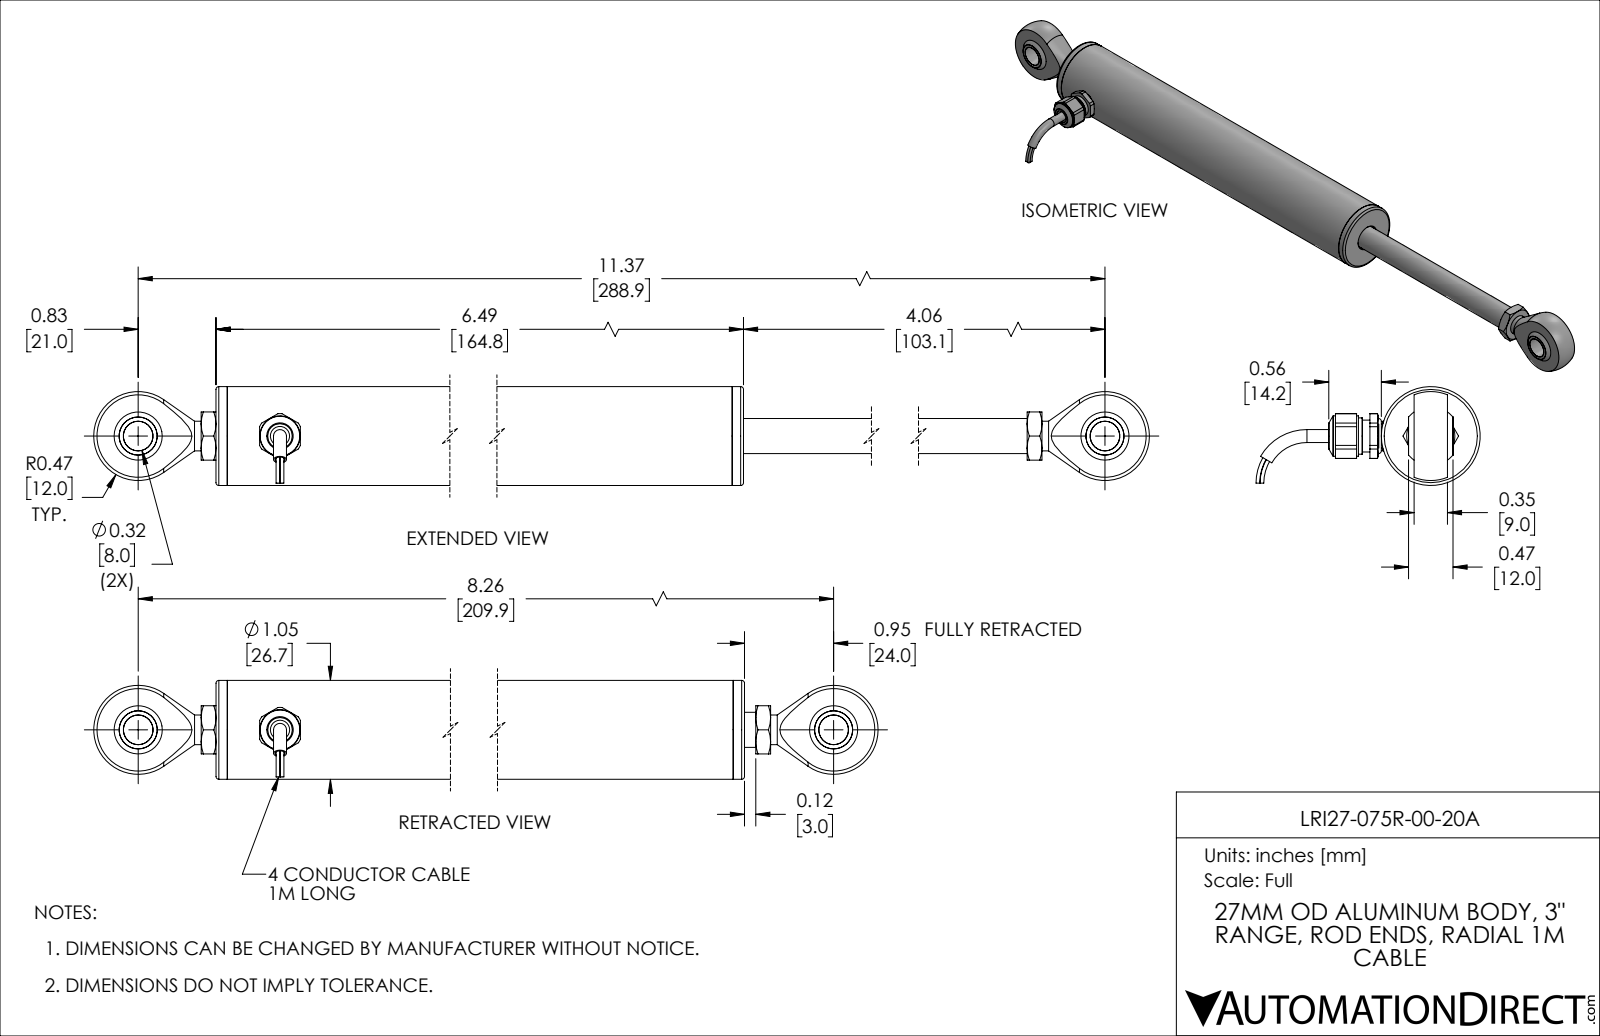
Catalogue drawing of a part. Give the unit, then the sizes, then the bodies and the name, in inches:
Units: inches
Overall size (bounding box): 9.208 × 2.382 × 1.05
Round holes (diameter × count): ⌀0.268 ×2, ⌀0.106 ×1, ⌀0.138 ×1, ⌀0.201 ×1, ⌀0.205 ×1, ⌀0.25 ×1, ⌀0.274 ×1, ⌀0.36 ×1, ⌀0.375 ×1, ⌀0.386 ×1, ⌀0.499 ×1, ⌀0.825 ×1
Round bosses / shafts (diameter × count): ⌀0.315 ×4, ⌀0.039 ×4, ⌀1.05 ×1, ⌀0.848 ×1, ⌀0.5 ×1, ⌀0.429 ×1, ⌀0.386 ×1, ⌀0.373 ×1
Partial cylindrical surfaces — rounded edges, fillets, slot ends (radius × count): R0.238 ×1
Main face-to-face distances: 0.12, 6.37, 0.354, 6.49, 6.25, 0.4, 0.28, 5.97, 6.09, 0.157
Volume: 3.621 in³ · Surface area: 72.73 in²
Bodies: 17 solids, 219 faces (82 planar, 57 cylindrical, 80 other)
Part name (STEP PRODUCT): LRI27-075R-00-20A
STEP written by: SolidWorks 2019 (AUTOMOTIVE_DESIGN)
